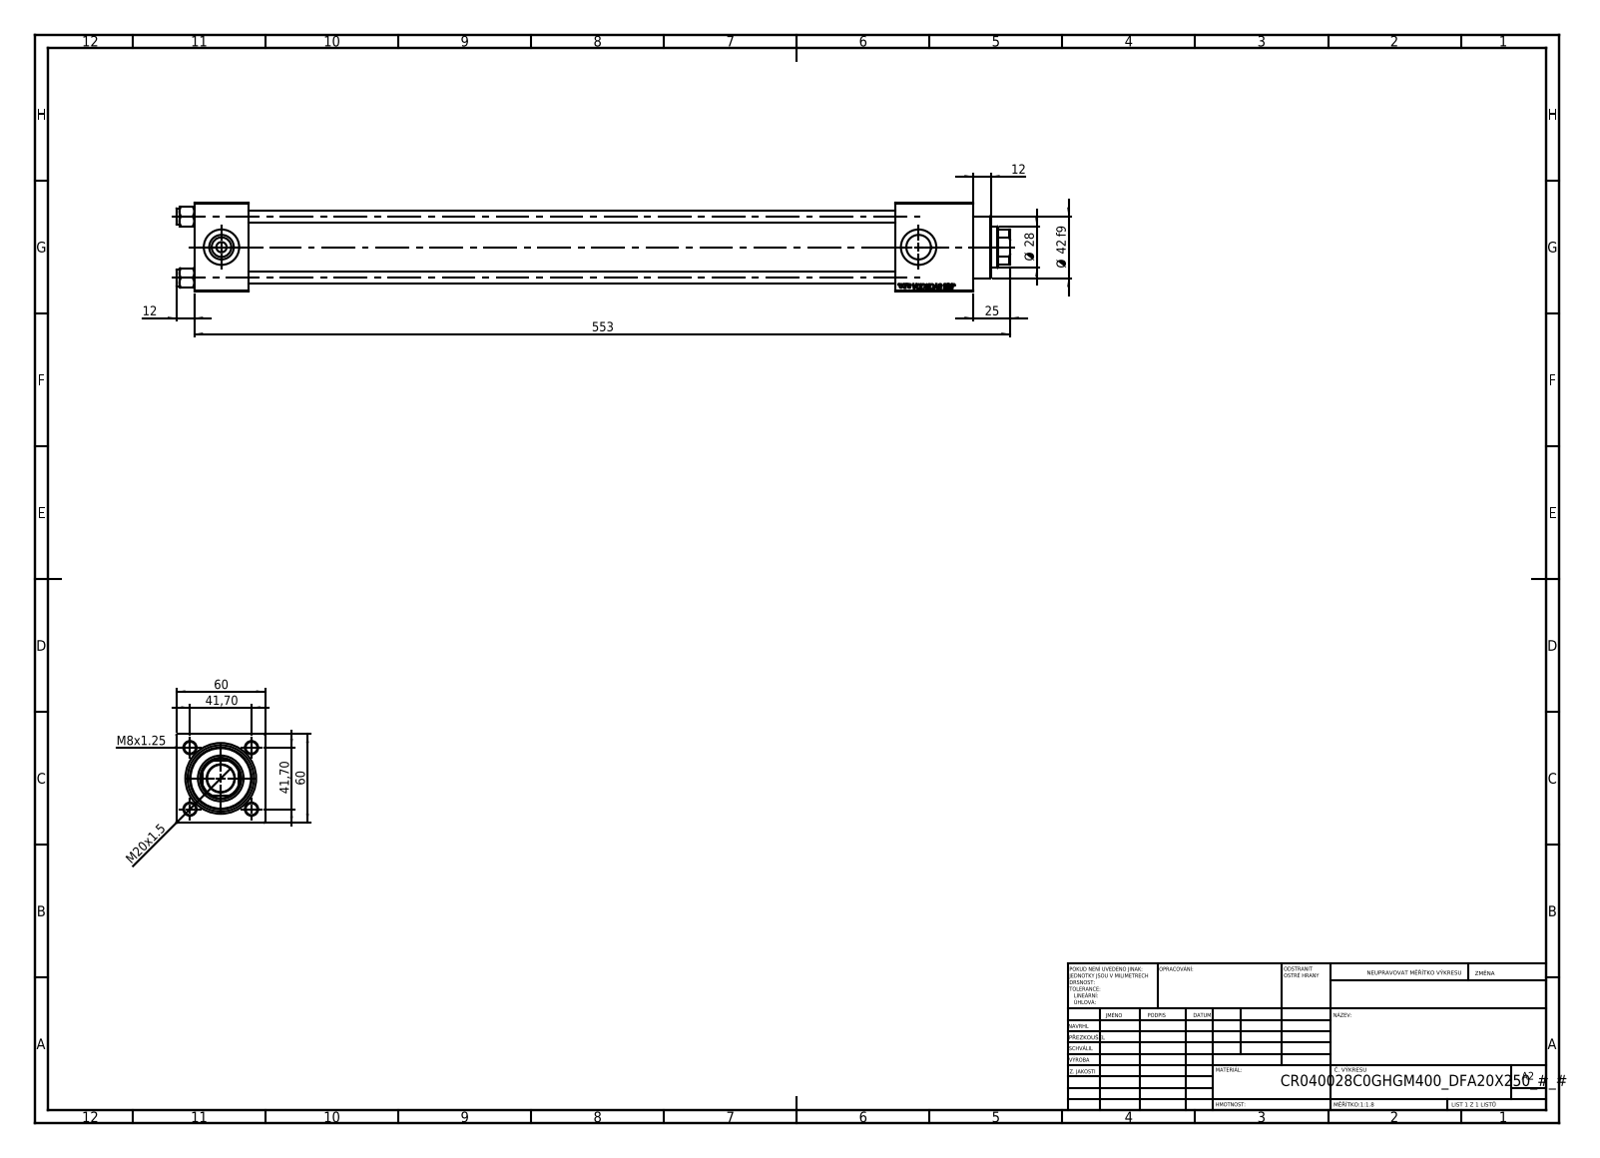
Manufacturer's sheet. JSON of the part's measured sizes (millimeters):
{"part_name": "V215CR_C_Body; V215CR_VCP_C; FEMALE_PART_FOR_DFA; NUT_M5_C (+2 more)", "step_written_by": "SolidWorks 2019 (CONFIG_CONTROL_DESIGN)", "units": "millimeters", "bodies": {"solids": 12, "faces": 1181, "planar": 538, "cylindrical": 95, "other": 548}, "overall_size": [565, 60, 60], "volume_mm3": 912858, "surface_area_mm2": 293380, "round_holes": [[8, 4], [7, 2], [16.66, 2], [24, 2], [18.5, 1], [28, 1], [31, 1], [40, 1], [45, 1]], "round_bosses_or_shafts": [[11, 4], [46, 1], [42, 1], [36, 1], [30, 1], [20, 1], [18, 1]], "partial_cylinders_radius": [[7.5, 1], [12, 1], [13.5, 1]], "face_to_face_distances": [60, 37, 475, 438, 499.3, 462.3, 24.3, 53, 528, 491], "hole_center_spacings": [29.49, 41.7, 58.97, 472.5]}
